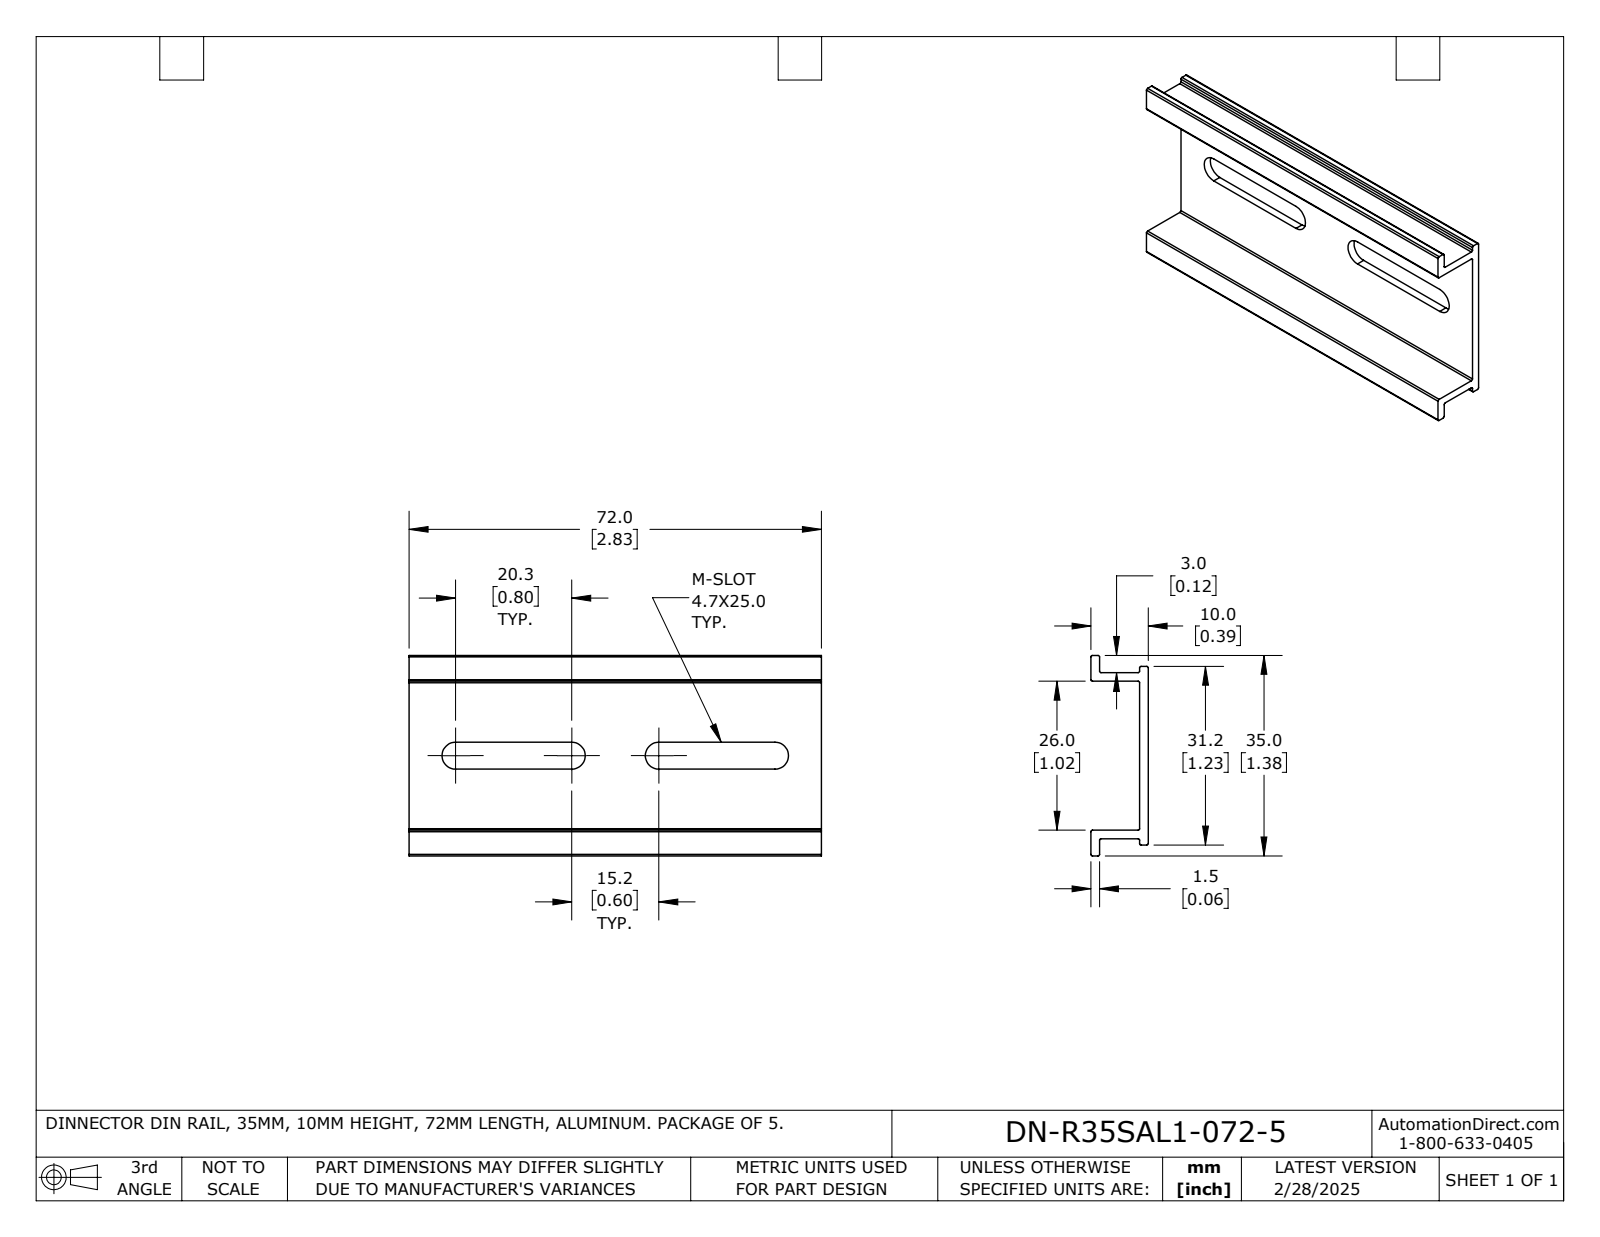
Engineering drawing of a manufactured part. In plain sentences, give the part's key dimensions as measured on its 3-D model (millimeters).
The part is named "DN-R35SAL1-072-5_Default". Its 3-D file was written by "SolidWorks 2024 (CONFIG_CONTROL_DESIGN)". It is 1 solid with 42 faces: 22 planar, 20 cylindrical and 0 other. Overall it measures 72 by 35 by 10 millimeters. Its volume is 5 511 cubic millimeters and its surface area 7 766 square millimeters. Partial cylindrical surfaces (rounded edges, fillets, slot ends): 16 of radius 0.27, 4 of radius 2.35. The main face-to-face distances are 1.5, 27.5, 8.5, 26, 10, 29, 7, 1.1, 2.6, 28.6.
